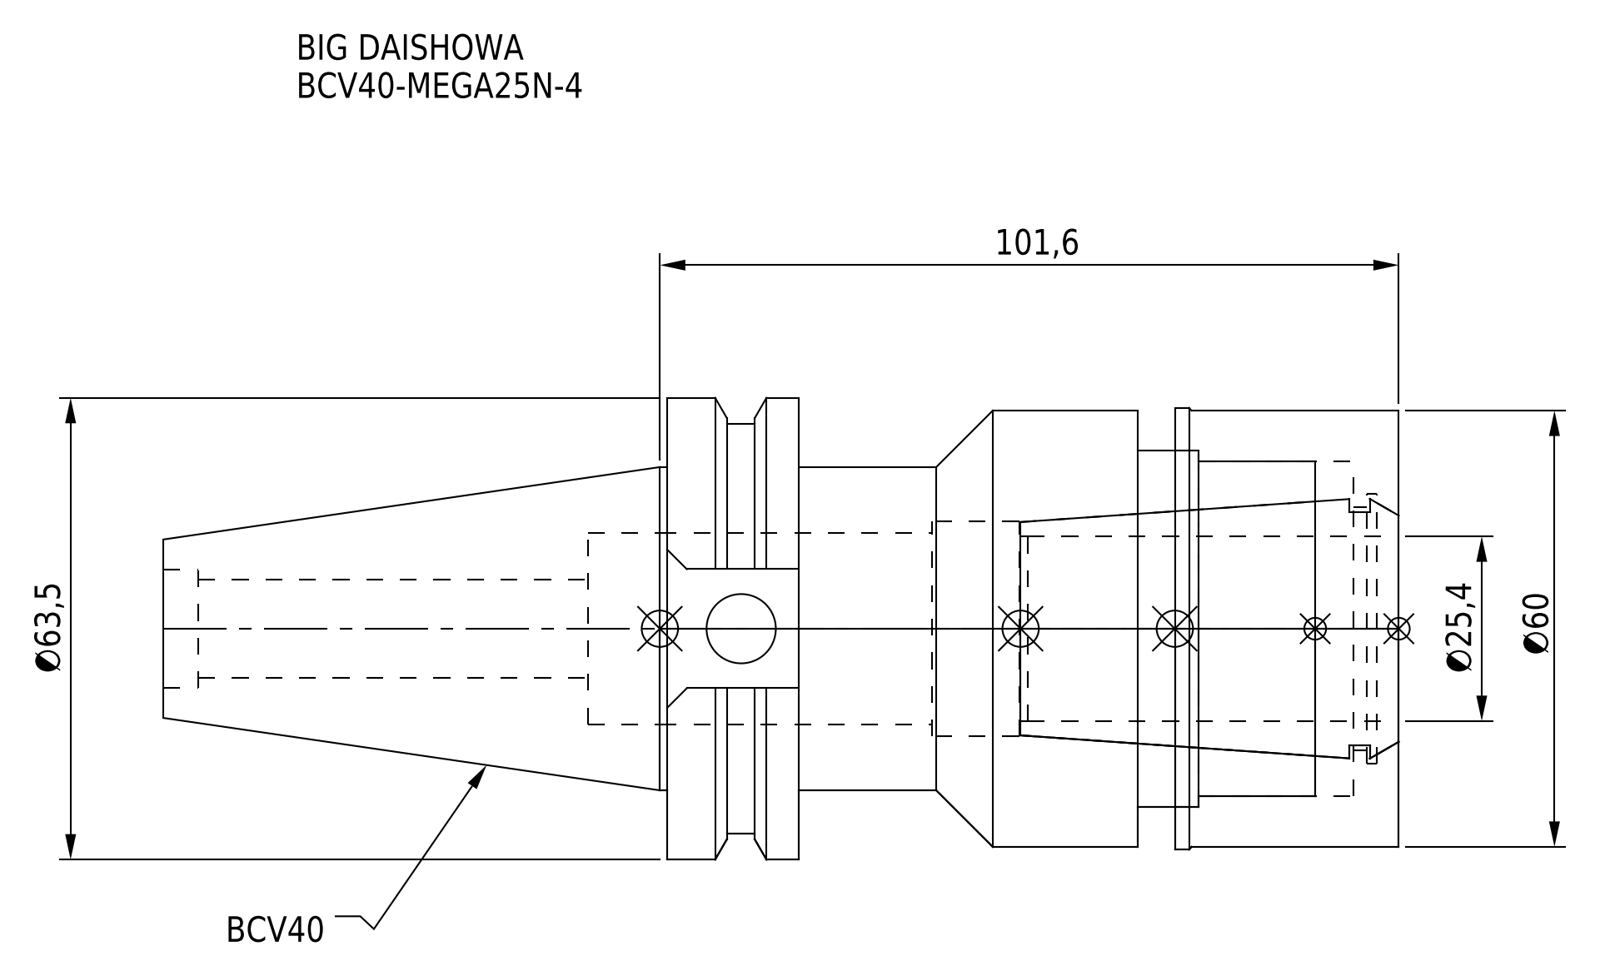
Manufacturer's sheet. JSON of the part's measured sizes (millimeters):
{"part_name": "BCV40-MEGA25N-4-254.stp; BCV40-MEGA25N-4_1.stp; BCV40-MEGA25N-4-254-FreeParts; DXF_TEMP_ASSY_ASM_4_ASM.stp (+3 more)", "step_written_by": "SolidWorks 2019 (CONFIG_CONTROL_DESIGN)", "units": "millimeters", "bodies": {"solids": 2, "faces": 85, "planar": 31, "cylindrical": 40, "other": 14}, "overall_size": [169.85, 63.5, 61.35], "volume_mm3": 225838, "surface_area_mm2": 55758, "round_holes": [[9.53, 1], [13.6, 1], [16.32, 1], [26.3, 1], [29.6, 1], [33.5, 1], [37.2, 1], [46, 1], [49, 1]], "round_bosses_or_shafts": [[63.5, 1], [60.7, 1], [60, 1], [56.36, 1], [44.45, 1]], "face_to_face_distances": [82.55, 100.6, 18.05, 30.8, 51.75, 69.8, 35.9, 5.1, 46.65, 64.7]}
